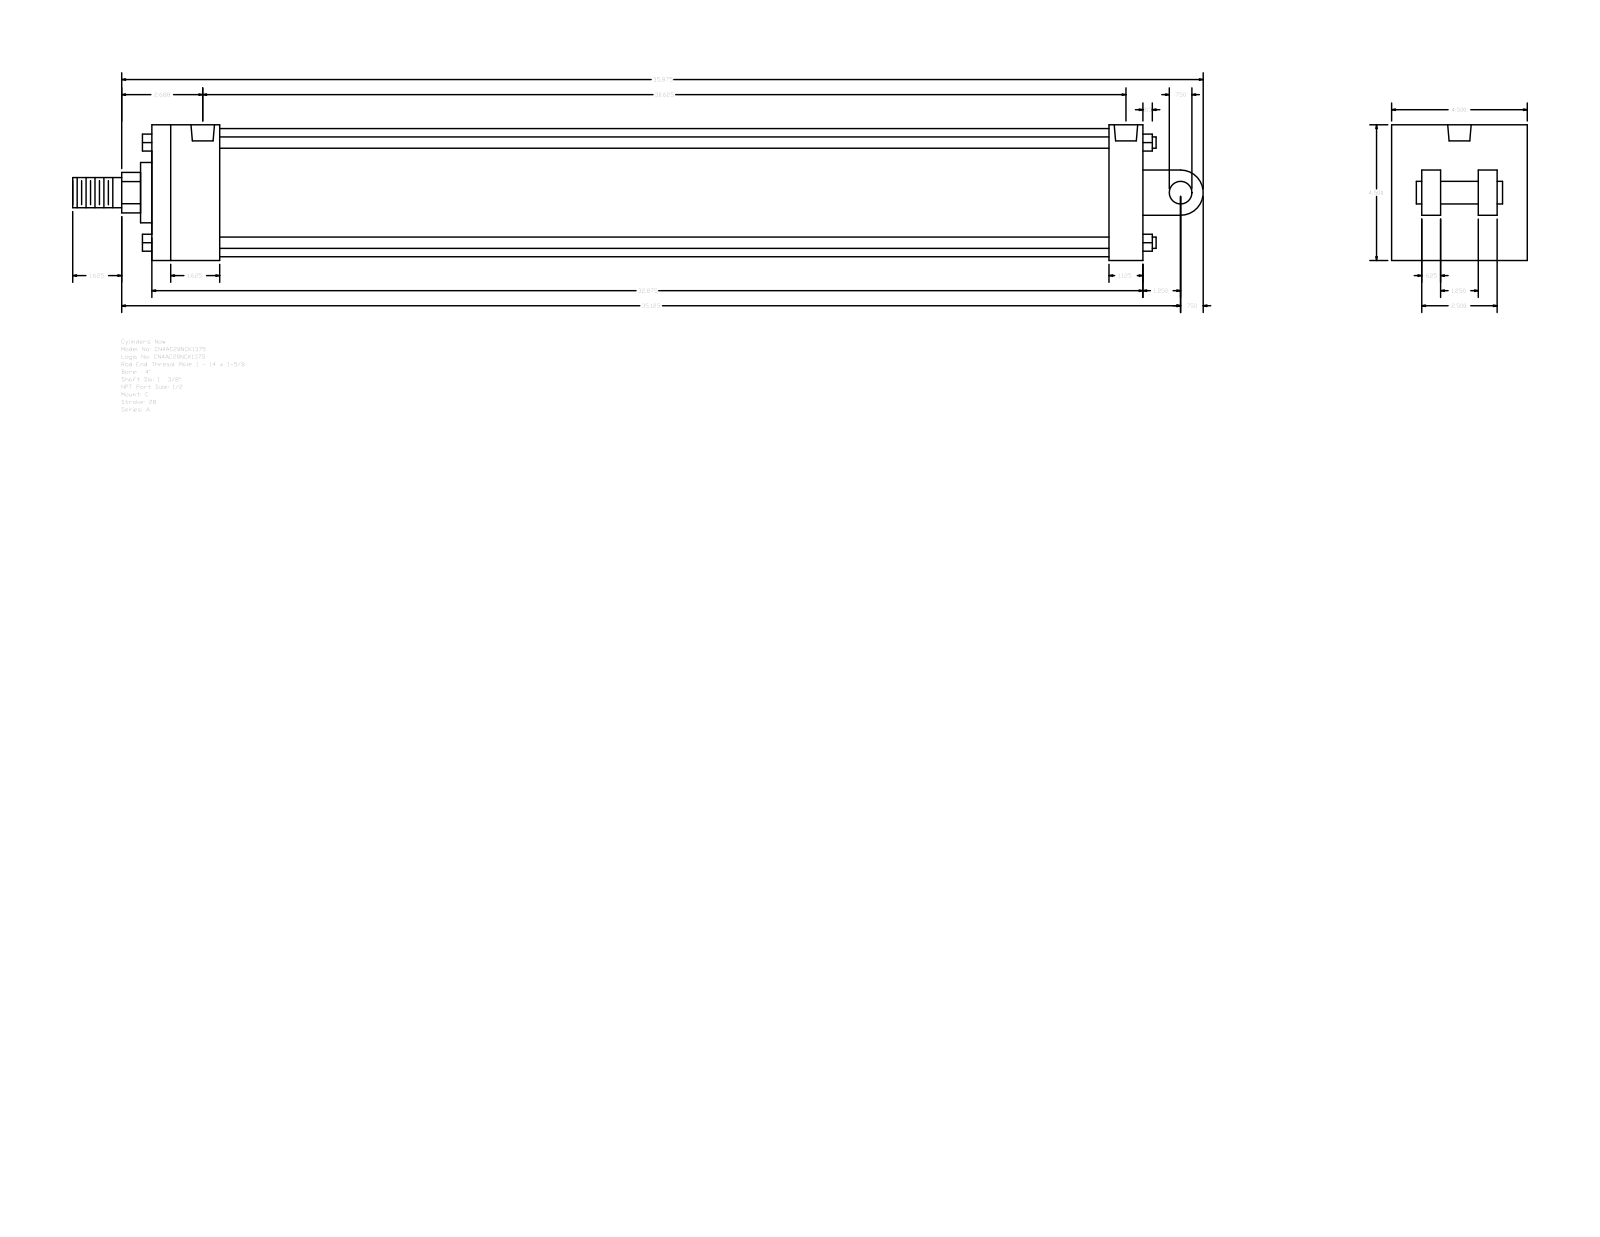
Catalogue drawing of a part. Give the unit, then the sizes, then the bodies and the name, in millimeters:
Units: millimetres
Overall size (bounding box): 952.5 × 114.3 × 114.3
Round holes (diameter × count): ⌀8.73 ×4, ⌀19.77 ×2
Round bosses / shafts (diameter × count): ⌀9.53 ×4, ⌀107.95 ×1, ⌀50.8 ×1, ⌀34.92 ×1, ⌀25.4 ×1, ⌀19.05 ×1
Partial cylindrical surfaces — rounded edges, fillets, slot ends (radius × count): R17.06 ×1, R19.05 ×1
Main face-to-face distances: 114.3, 835.02, 57.15, 73.03, 806.45, 28.57, 749.3, 777.87, 41.27, 25.4
Hole centre spacings: 3.18, 771.52, 774.7, 777.88
Bodies: 0 solids, 135 faces (102 planar, 33 cylindrical, 0 other)
Part name (STEP PRODUCT): A_C__0400_1.375
STEP written by: GSSL Pune (CONFIG_CONTROL_DESIGN)
